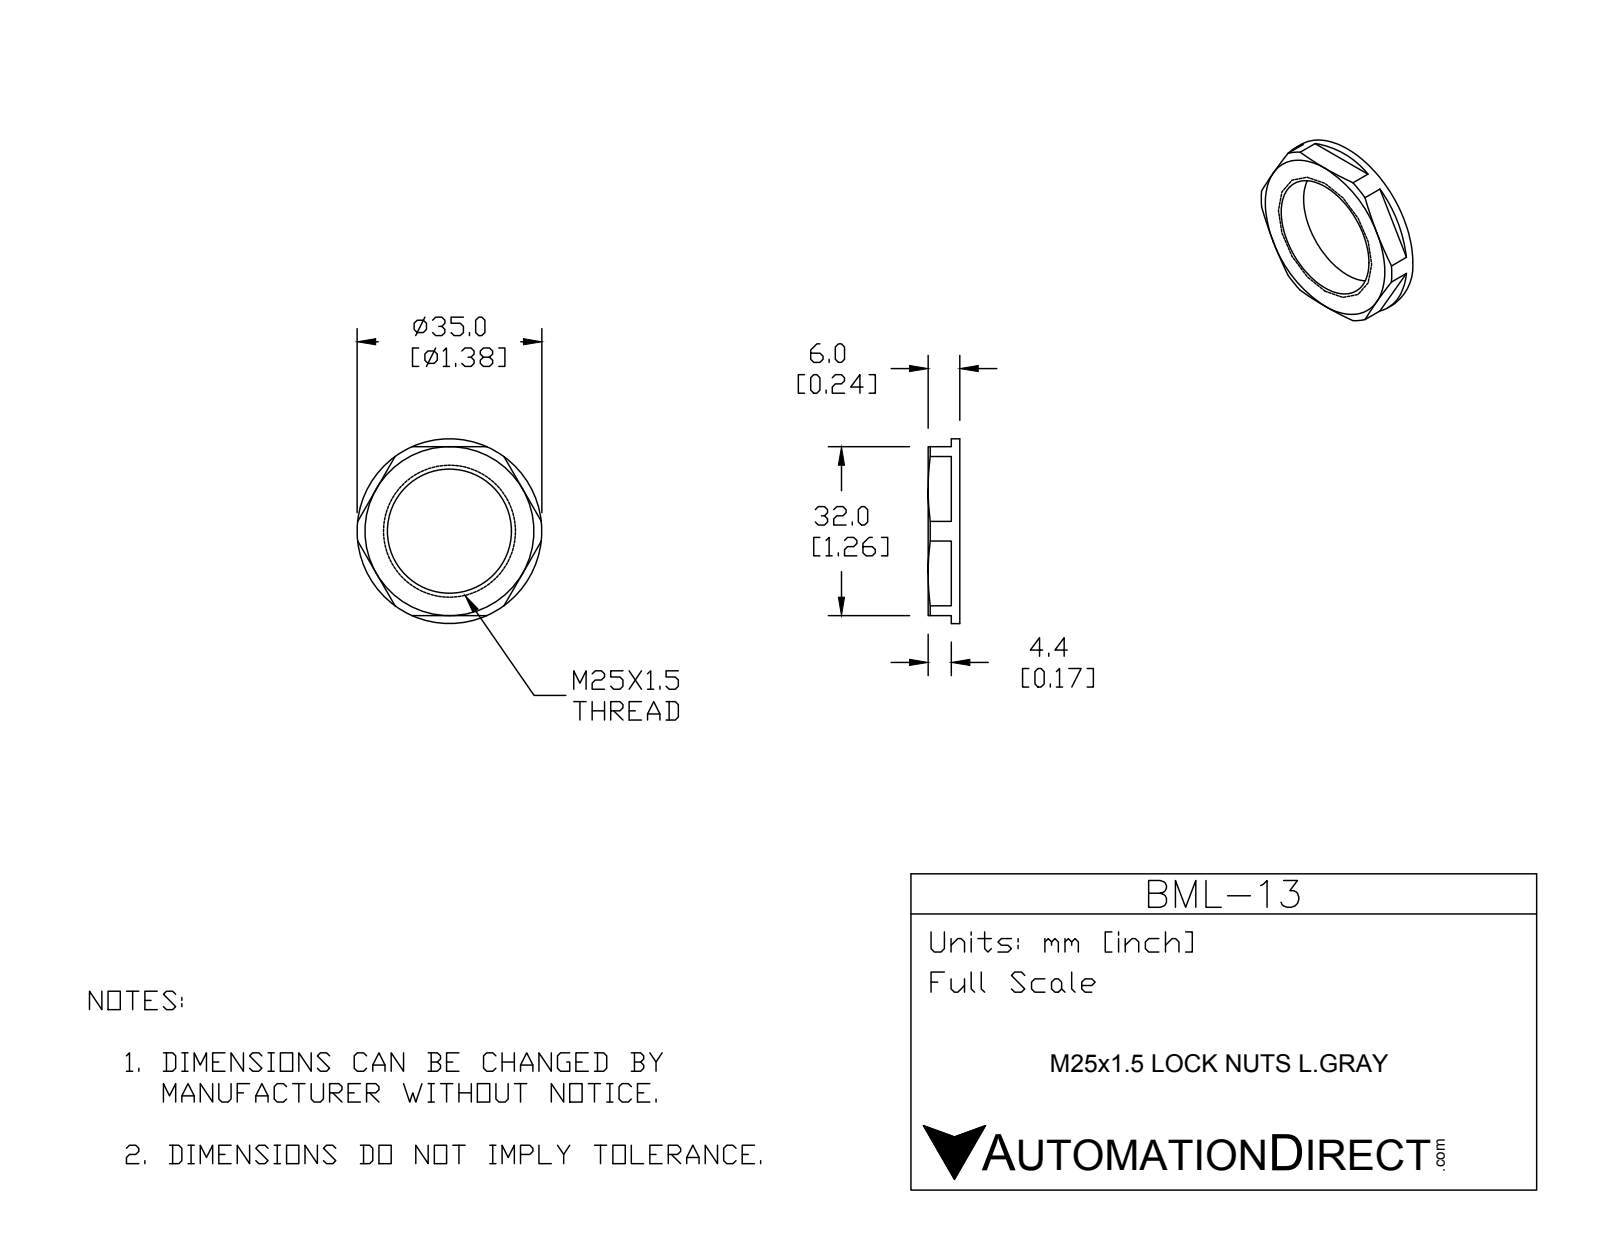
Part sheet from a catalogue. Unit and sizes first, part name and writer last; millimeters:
Units: millimetres
Overall size (bounding box): 35 × 35 × 6
Round holes (diameter × count): ⌀1.5 ×3, ⌀23.5 ×1
Round bosses / shafts (diameter × count): ⌀35 ×1
Main face-to-face distances: 6, 32, 1.6, 4.4, 1.3, 5.7
Hole centre spacings: 16.05, 27.8
Volume: 2 780 mm³ · Surface area: 2 135 mm²
Bodies: 1 solid, 33 faces (17 planar, 10 cylindrical, 6 other)
Part name (STEP PRODUCT): BML-13
STEP written by: SolidWorks 2015 (CONFIG_CONTROL_DESIGN)
